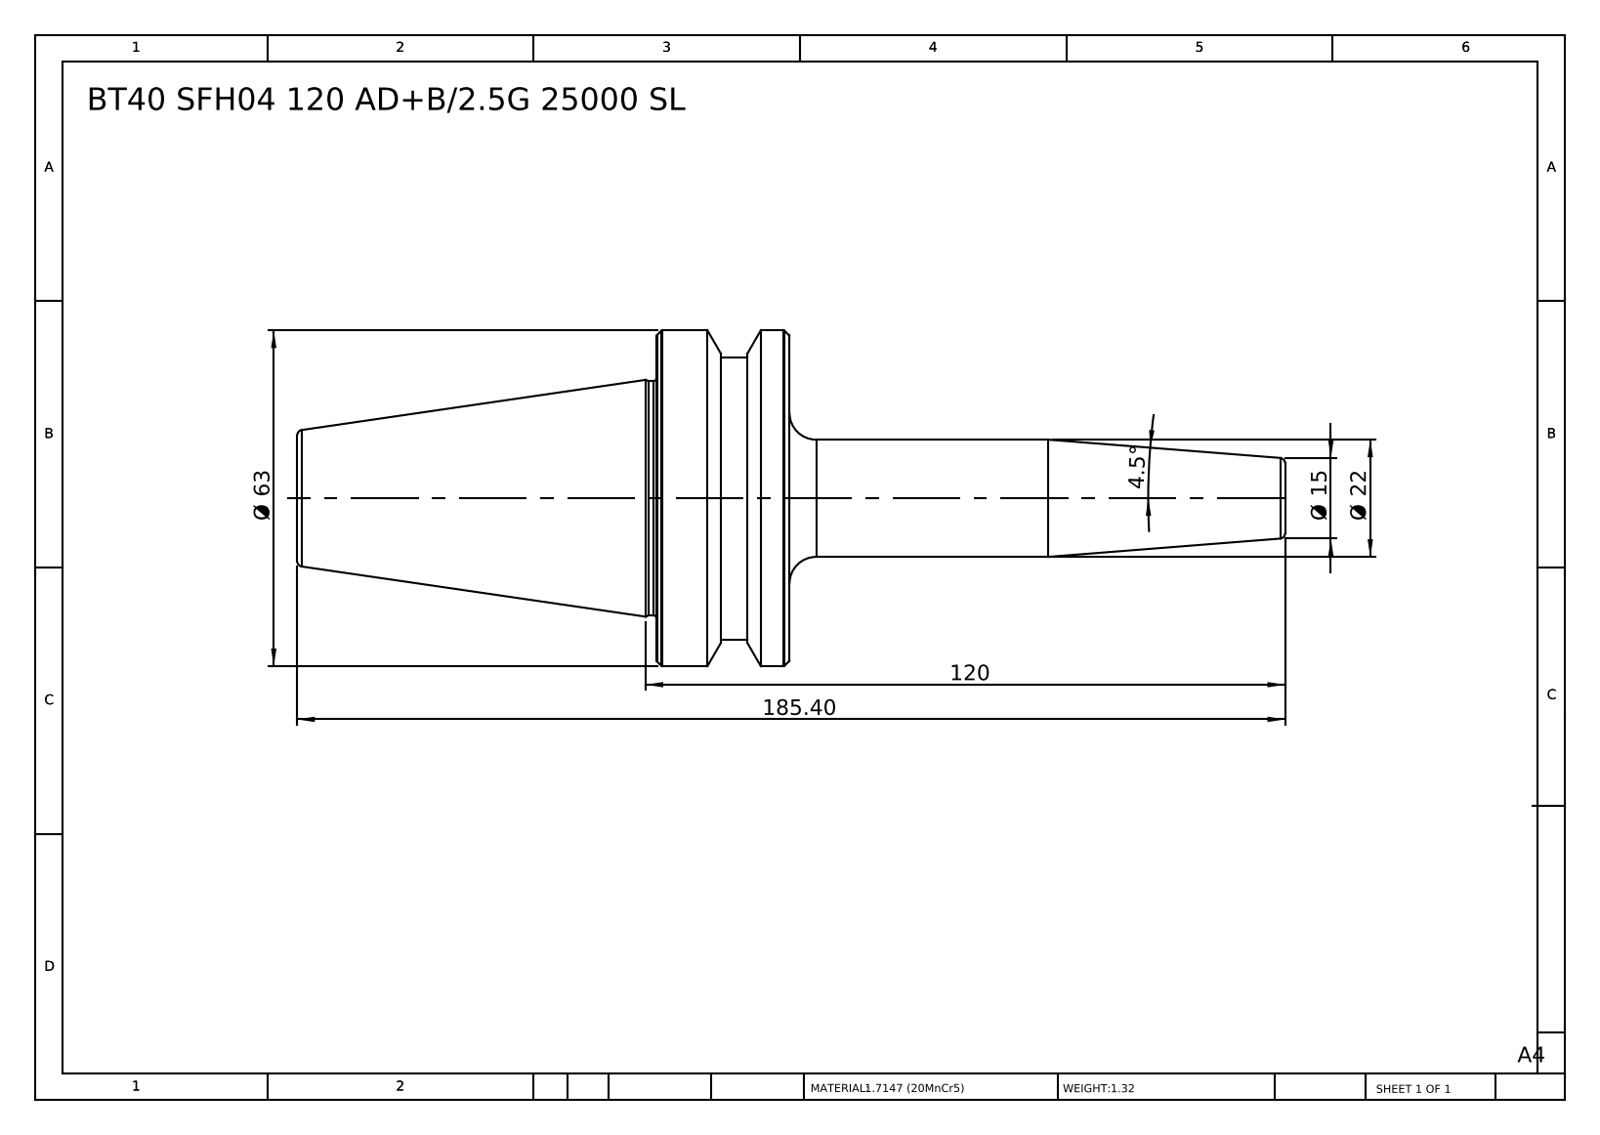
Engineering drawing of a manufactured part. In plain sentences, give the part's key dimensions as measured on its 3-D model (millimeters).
The part is named "BT40 SFH04 120 AD+B-2.5G 25000 SL". Its 3-D file was written by "SolidWorks 2014 (CONFIG_CONTROL_DESIGN)". It is 1 solid with 46 faces: 6 planar, 10 cylindrical and 30 other. Overall it measures 185.4 by 63 by 63 millimeters. Its volume is 169 286 cubic millimeters and its surface area 23 910 square millimeters. Round bosses or shafts: 1 of diameter 63, 1 of diameter 53, 1 of diameter 44, 1 of diameter 22. The main face-to-face distances are 25, 92.4, 67.4, 93, 118, 185.4, 100.9, 7.9, 17.1, 84.5.
